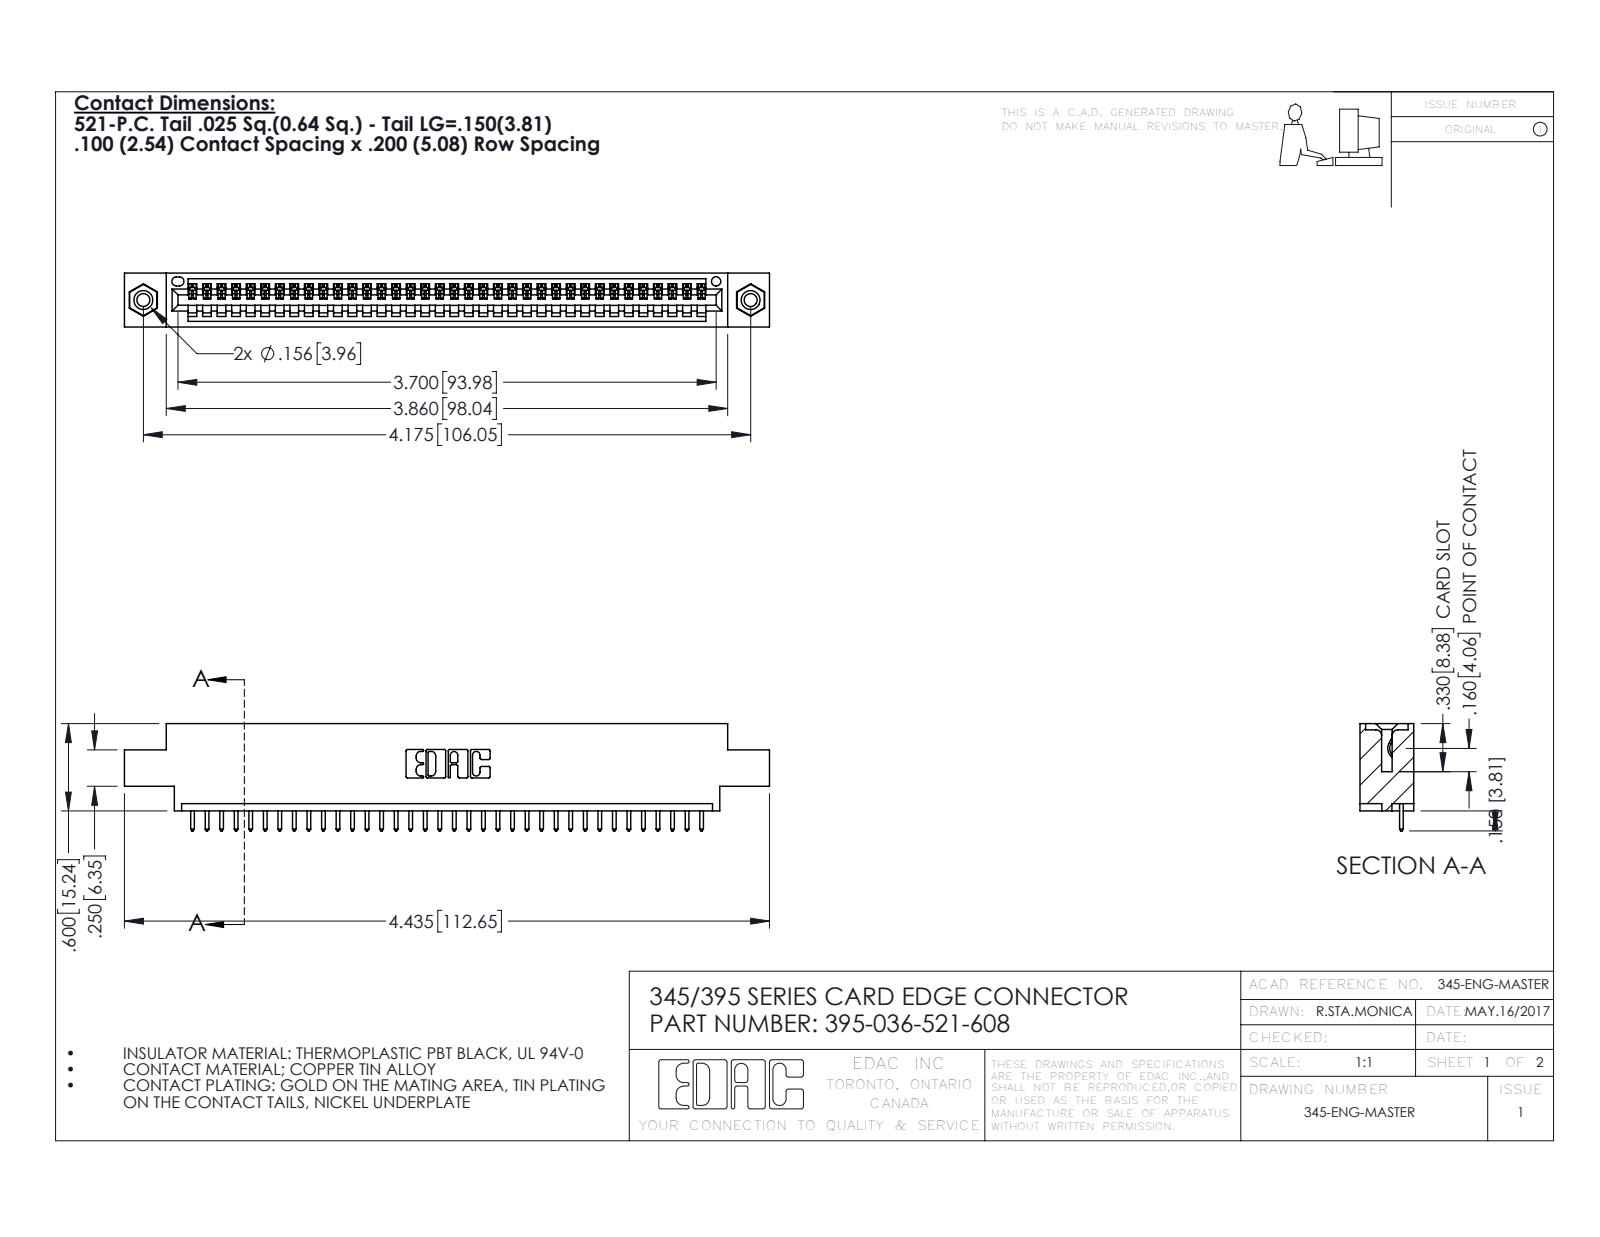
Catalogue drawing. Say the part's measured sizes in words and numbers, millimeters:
The part is named "395-036-521-608; 345-250-001_345-250-003-102; 345 Part_0.170 Offset - 0.156 Dia-TI; 345-292-001_345-293-121". Its 3-D file was written by "SolidWorks 2016 (CONFIG_CONTROL_DESIGN)". It is 39 solids with 2278 faces: 1556 planar, 706 cylindrical and 16 other. Overall it measures 112.6 by 18.7 by 9.4 millimeters. Its volume is 10 400 cubic millimeters and its surface area 13 520 square millimeters. Round holes: 2 of diameter 2.3, 2 of diameter 3.2, 2 of diameter 4, 1 of diameter 1.6. Round bosses or shafts: 2 of diameter 3.9. Partial cylindrical surfaces (rounded edges, fillets, slot ends): 72 of radius 0.2, 72 of radius 0.3, 22 of radius 0.3, 6 of radius 0.2, 6 of radius 0.8, 3 of radius 0.7, 2 of radius 0.8, 2 of radius 1. The main face-to-face distances are 1.8, 7.6, 9.4, 5.1, 2.5, 6.9, 0.6, 5.7, 4.4, 3.8. The hole center spacings are 6.9, 100.1, 106.
